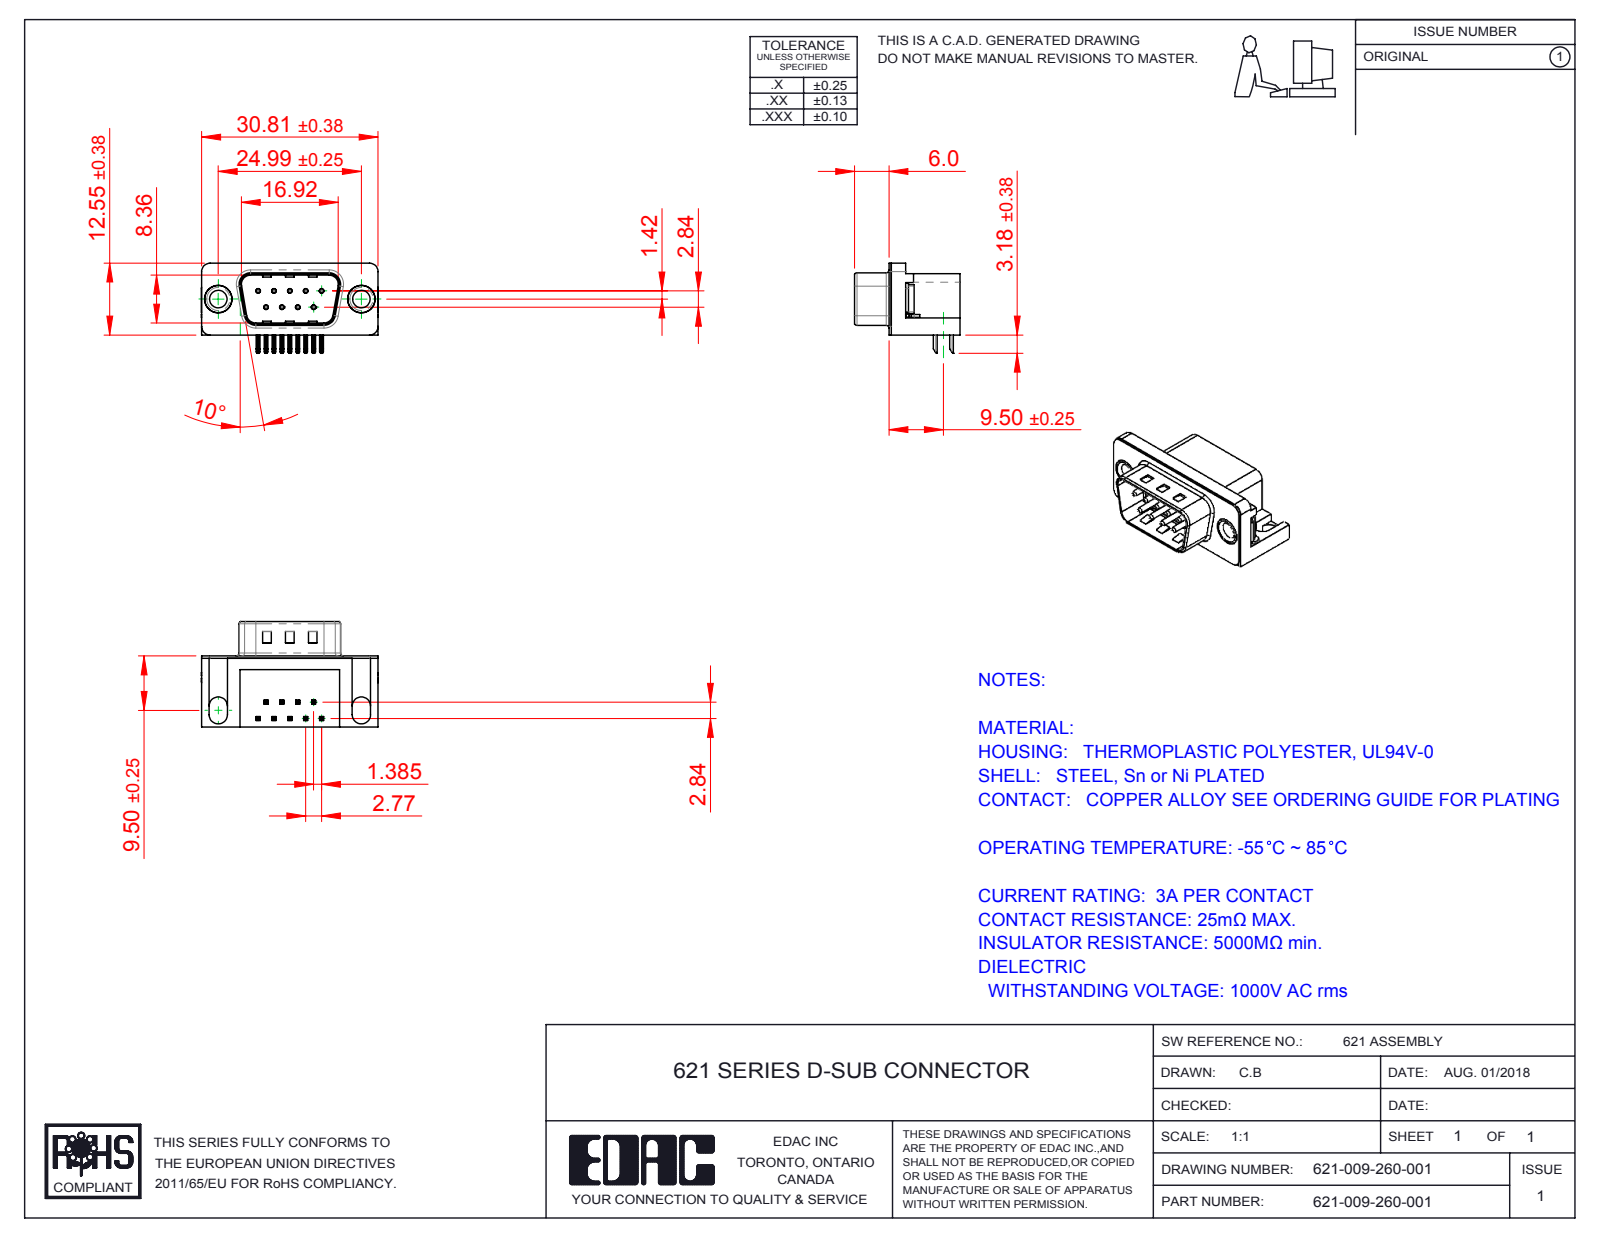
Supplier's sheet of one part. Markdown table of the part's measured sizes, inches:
| quantity | value |
| --- | --- |
| part name | 621 Contact Top; 621 Contact Bottom; 621 Shell_9 Socket; 621 Housing_9 Socket (+3 more) |
| STEP written by | SolidWorks 2016 (CONFIG_CONTROL_DESIGN) |
| units | inches |
| bodies | 15 solids, 945 faces (571 planar, 293 cylindrical, 81 other) |
| overall size | 1.216 × 0.724 × 0.619 |
| volume | 0.195 in³ |
| surface area | 6.549 in² |
| round holes (diameter × count) | 0.014 × 9, 0.031 × 9, 0.12 × 2, 0.157 × 2, 0.189 × 2, 0.197 × 2 |
| round bosses / shafts (diameter × count) | 0.03 × 9, 0.193 × 2, 0.187 × 2, 0.152 × 2 |
| partial cylindrical surfaces (radius × count) | 0.01 × 44, 0.005 × 18, 0.039 × 16, 0.02 × 9, 0.059 × 8, 0.063 × 8, 0.035 × 4, 0.079 × 4 |
| main face-to-face distances | 0.016, 0.472, 0.488, 0.407, 0.114, 0.374, 0.098, 0.083, 0.014, 0.421 |
| hole center spacings | 0.124, 0.109, 0.218, 0.198, 0.198, 0.327, 0.294, 0.295 |
